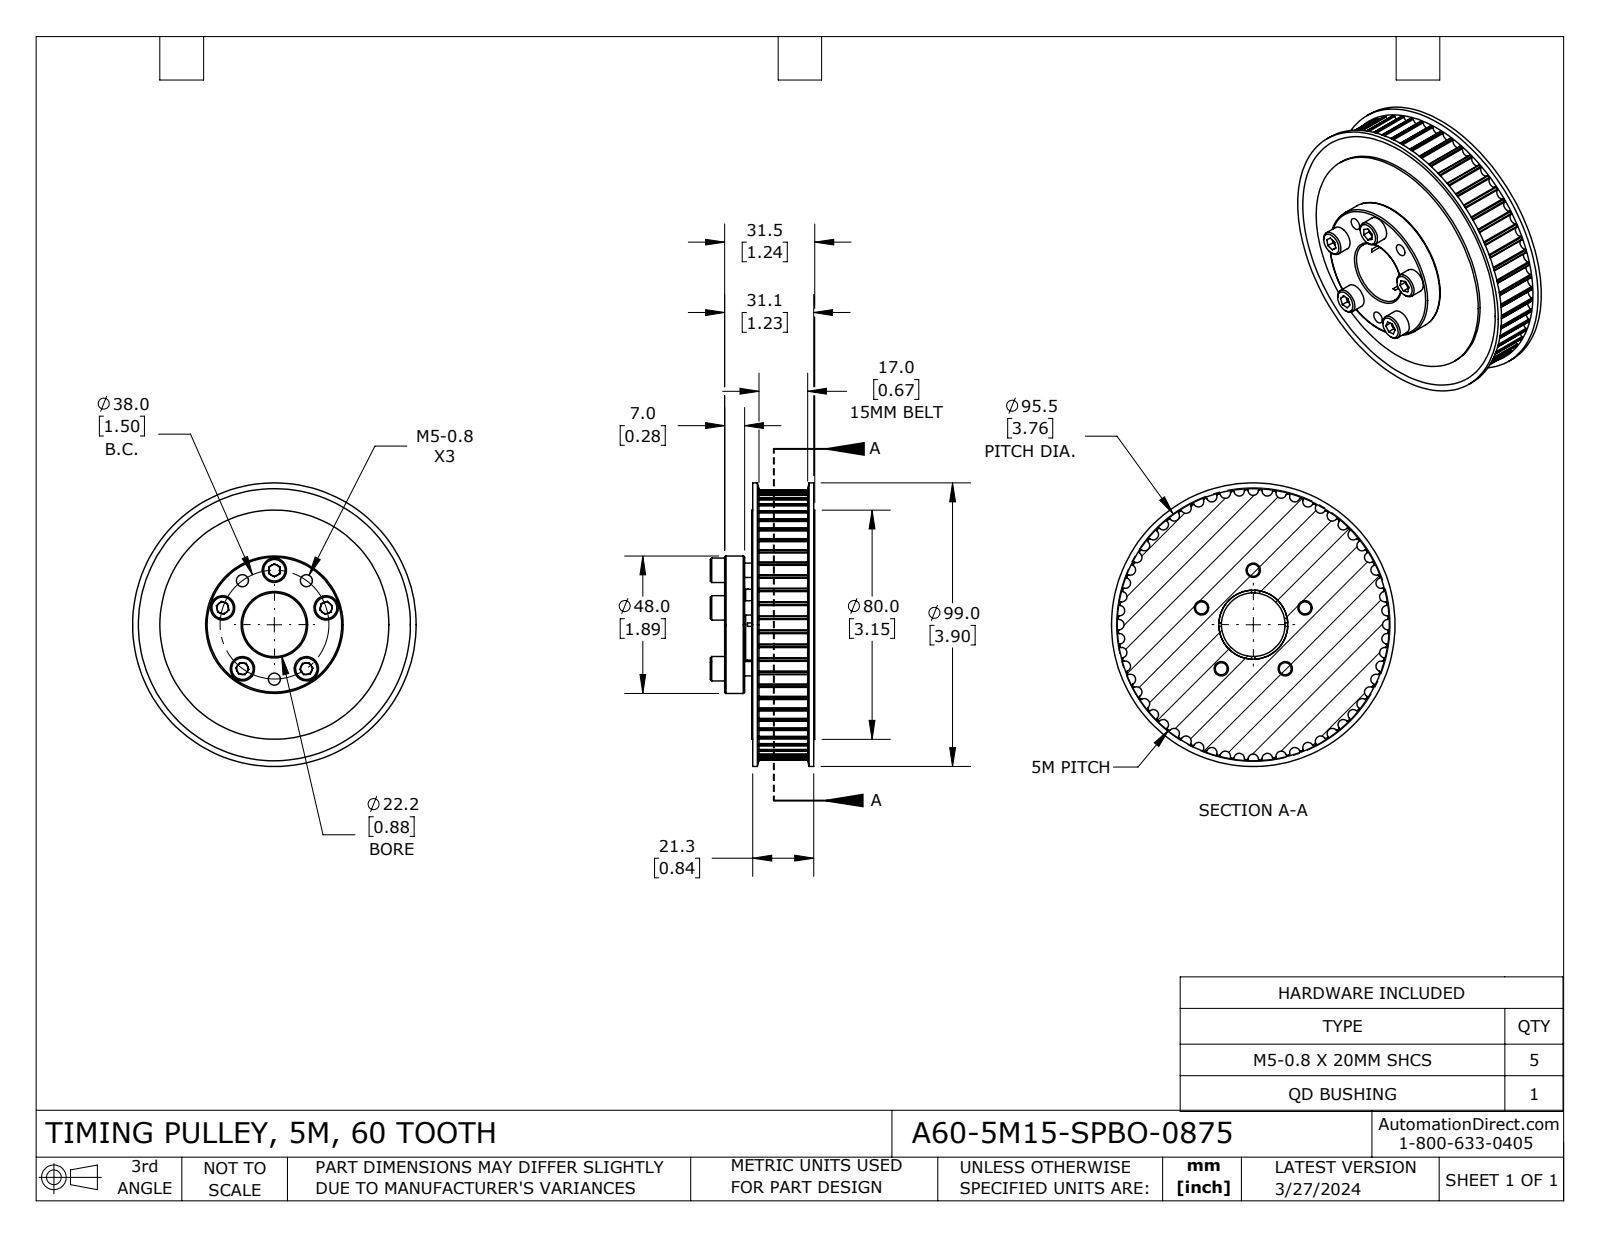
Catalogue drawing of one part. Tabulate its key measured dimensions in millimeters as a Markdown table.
| quantity | value |
| --- | --- |
| part name | A60-5M15-SPBO-0875 |
| STEP written by | SolidWorks 2021 (CONFIG_CONTROL_DESIGN) |
| units | millimeters |
| bodies | 9 solids, 534 faces (101 planar, 367 cylindrical, 66 other) |
| overall size | 99 × 99 × 36.5 |
| volume | 148 845 mm³ |
| surface area | 46 210 mm² |
| round holes (diameter × count) | 4.2 × 8, 5.5 × 5, 22.22 × 1, 24.83 × 1, 80 × 1 |
| round bosses / shafts (diameter × count) | 8.5 × 5, 5 × 5, 99 × 1, 48 × 1, 24.82 × 1 |
| partial cylindrical surfaces (radius × count) | 0.3 × 120, 1.82 × 60, 47.17 × 1 |
| main face-to-face distances | 2.5, 19.5, 22, 0.9, 21.1, 1.6, 18.6, 17, 20.2, 12 |
| hole center spacings | 19, 36.14, 30.74, 11.75, 22.34, 38, 11.74, 22.33 |
